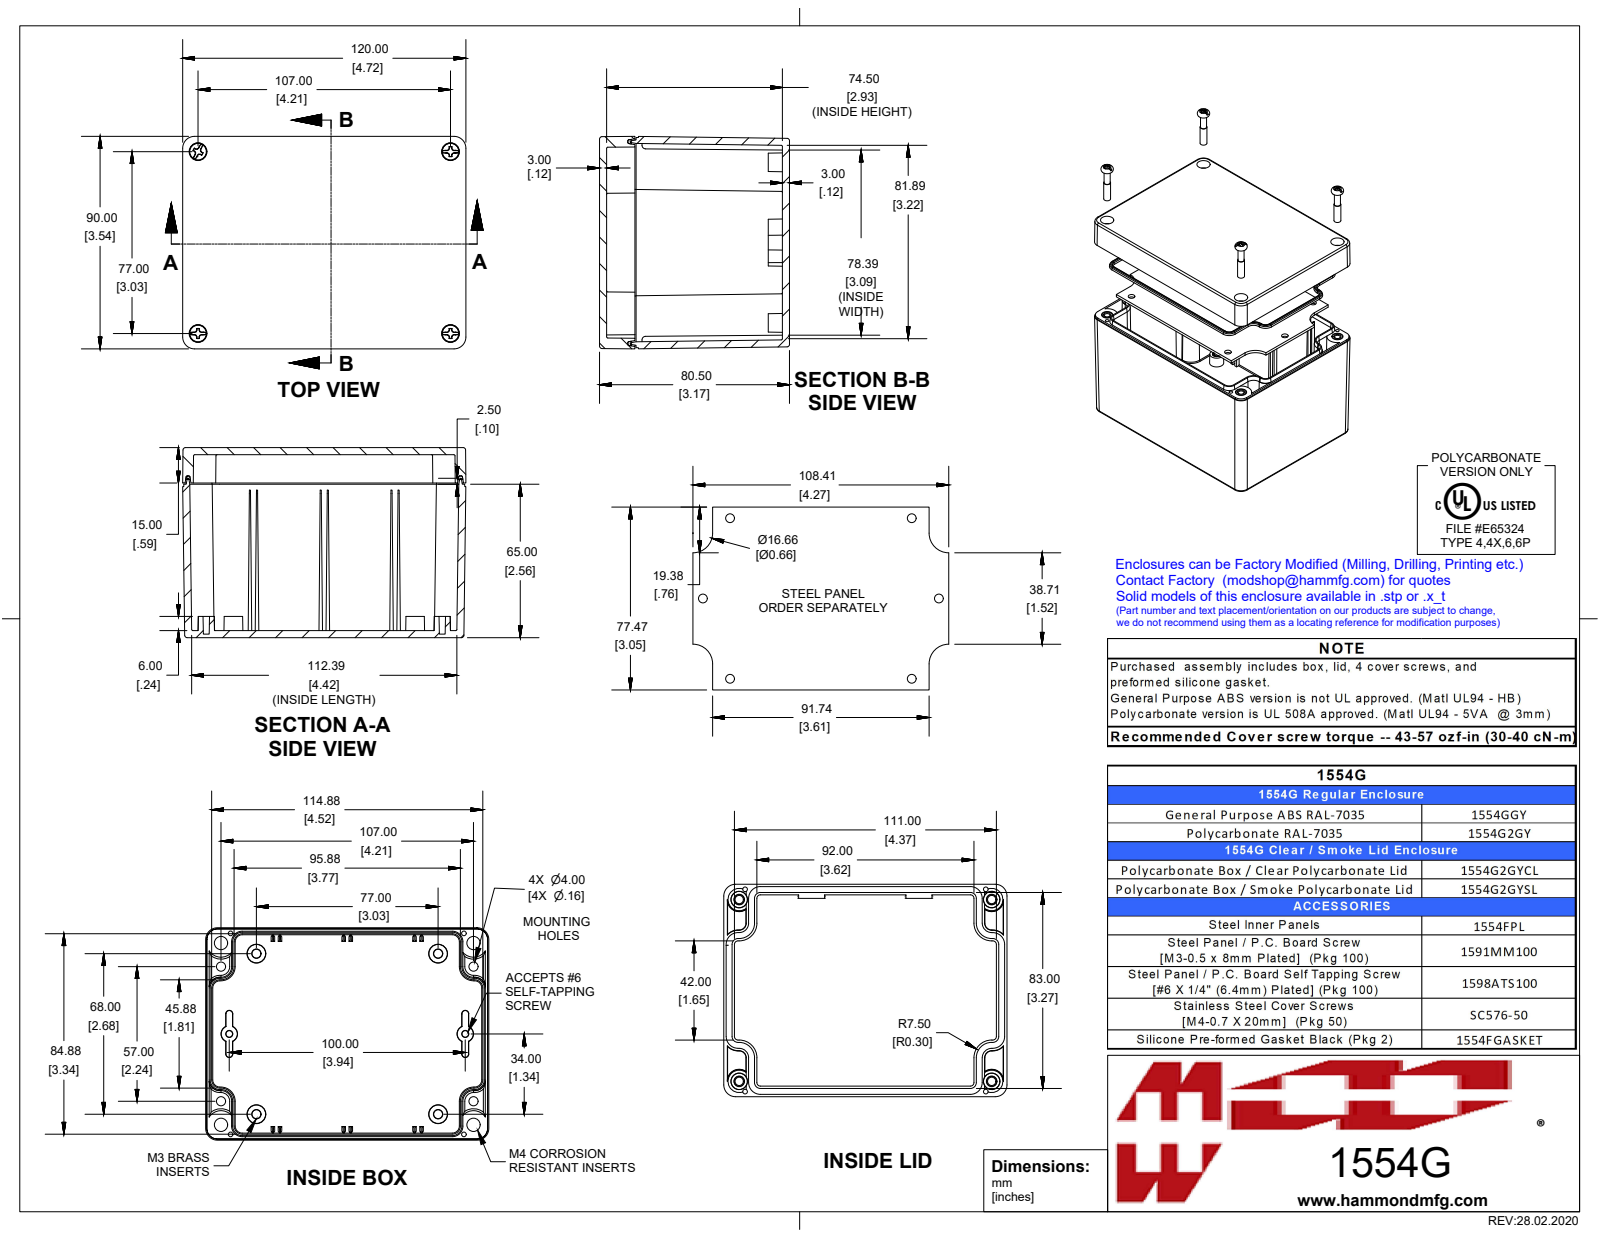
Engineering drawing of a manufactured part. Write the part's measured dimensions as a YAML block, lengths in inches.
part_name: "1554G2GY"
step_written_by: "SolidWorks 2019 (AUTOMOTIVE_DESIGN)"
units: inches
bodies: {solids: 16, faces: 1384, planar: 396, cylindrical: 358, other: 630}
overall_size: [4.724, 3.543, 3.169]
volume: 11.95
surface_area: 232.7
round_holes:
  - {diameter: 0.079, count: 8}
  - {diameter: 0.097, count: 4}
  - {diameter: 0.128, count: 4}
  - {diameter: 0.138, count: 4}
  - {diameter: 0.147, count: 4}
  - {diameter: 0.276, count: 4}
  - {diameter: 0.11, count: 2}
round_bosses_or_shafts:
  - {diameter: 0.25, count: 4}
  - {diameter: 0.218, count: 4}
  - {diameter: 0.21, count: 4}
  - {diameter: 0.19, count: 4}
  - {diameter: 0.154, count: 4}
  - {diameter: 0.153, count: 4}
  - {diameter: 0.15, count: 4}
  - {diameter: 0.135, count: 4}
partial_cylinders:
  - {radius: 0.02, count: 36}
  - {radius: 0.039, count: 8}
  - {radius: 0.197, count: 8}
  - {radius: 0.187, count: 4}
  - {radius: 0.328, count: 4}
  - {radius: 0.059, count: 2}
face_to_face_distances: [0.118, 3.051, 3.169, 0.354, 2.697, 0.059, 0.236, 2.815, 2.933, 0.419]
hole_center_spacings: [0.197, 0.602, 0.617, 1.413, 1.522, 1.687, 2.915, 3.031]
